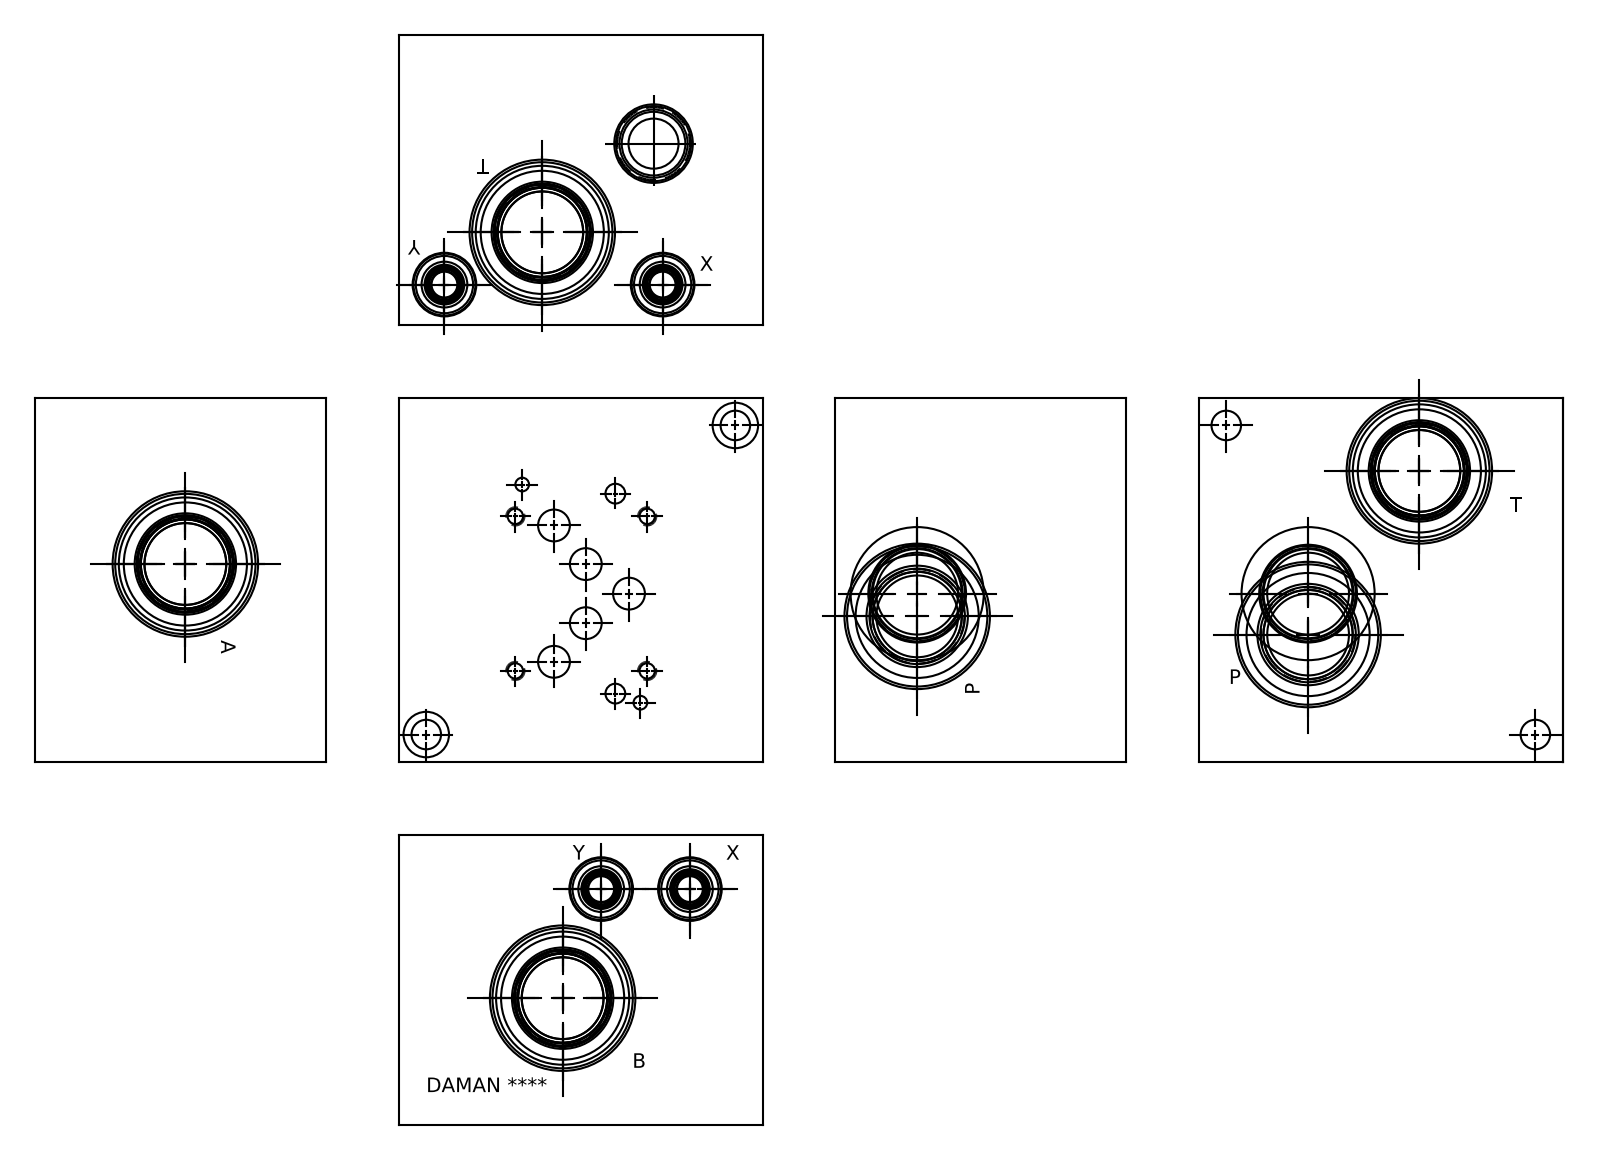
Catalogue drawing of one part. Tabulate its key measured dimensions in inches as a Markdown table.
| quantity | value |
| --- | --- |
| part name | Part__D05JSPRVS16S_3D |
| STEP written by | Autodesk Inventor 2020 (AUTOMOTIVE_DESIGN) |
| units | inches |
| bodies | 1 solid, 703 faces (386 planar, 86 cylindrical, 231 other) |
| overall size | 5 × 5 × 4 |
| volume | 81.59 in³ |
| surface area | 197.1 in² |
| round holes (diameter × count) | 0.438 × 9, 1.125 × 6, 1.231 × 6, 1.329 × 6, 1.934 × 6, 1.313 × 5, 1.398 × 5, 0.188 × 4, 0.201 × 4, 0.25 × 4, 0.375 × 4, 0.389 × 4 |
| main face-to-face distances | 5, 4, 0.031, 4.969, 4.938, 0.188, 3.812, 0.75, 4.219, 0.781 |
| hole center spacings | 0.688, 0.72, 1.413, 1.76, 1.774, 1.891, 2.477, 0.337 |
